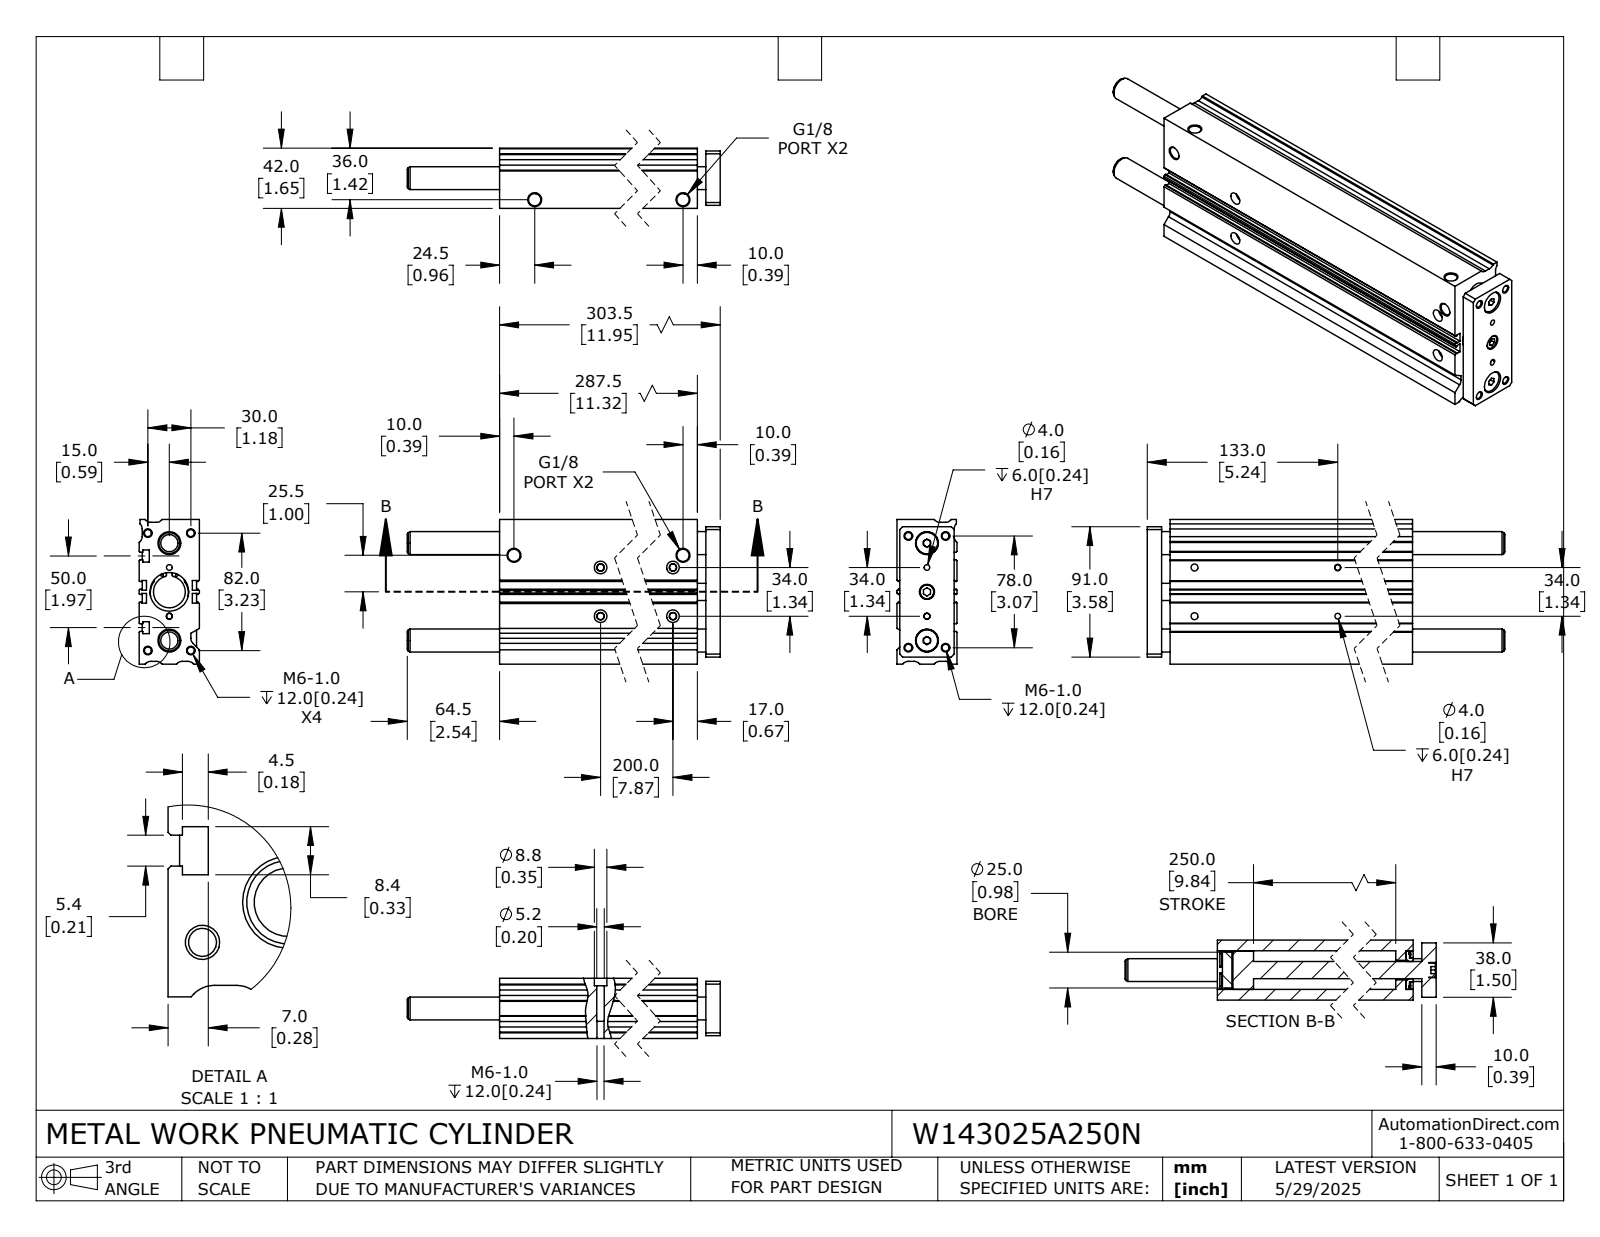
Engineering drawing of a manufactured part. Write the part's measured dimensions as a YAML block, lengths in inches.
part_name: "W143025A250N_ROD; W143025A250N; W143025A250N_BODY"
step_written_by: "SolidWorks 2024 (CONFIG_CONTROL_DESIGN)"
units: inches
bodies: {solids: 6, faces: 390, planar: 191, cylindrical: 157, other: 42}
overall_size: [14.488, 3.976, 1.654]
volume: 64.01
surface_area: 369.2
round_holes:
  - {diameter: 0.194, count: 8}
  - {diameter: 0.067, count: 4}
  - {diameter: 0.157, count: 4}
  - {diameter: 0.194, count: 4}
  - {diameter: 0.205, count: 4}
  - {diameter: 0.337, count: 4}
  - {diameter: 0.346, count: 4}
  - {diameter: 0.63, count: 2}
  - {diameter: 0.413, count: 1}
  - {diameter: 0.472, count: 1}
  - {diameter: 0.539, count: 1}
  - {diameter: 0.874, count: 1}
round_bosses_or_shafts:
  - {diameter: 0.61, count: 2}
  - {diameter: 1.063, count: 1}
  - {diameter: 0.984, count: 1}
  - {diameter: 0.65, count: 1}
  - {diameter: 0.394, count: 1}
partial_cylinders:
  - {radius: 0.039, count: 12}
  - {radius: 0.197, count: 9}
  - {radius: 0.079, count: 8}
  - {radius: 0.524, count: 2}
  - {radius: 0.559, count: 1}
face_to_face_distances: [1.654, 0.079, 0.197, 1.378, 1.457, 0.839, 3.976, 2.299, 0.276, 0.354]
hole_center_spacings: [1.339, 0.111, 0.29, 0.5, 0.548, 0.652, 0.669, 0.902]
